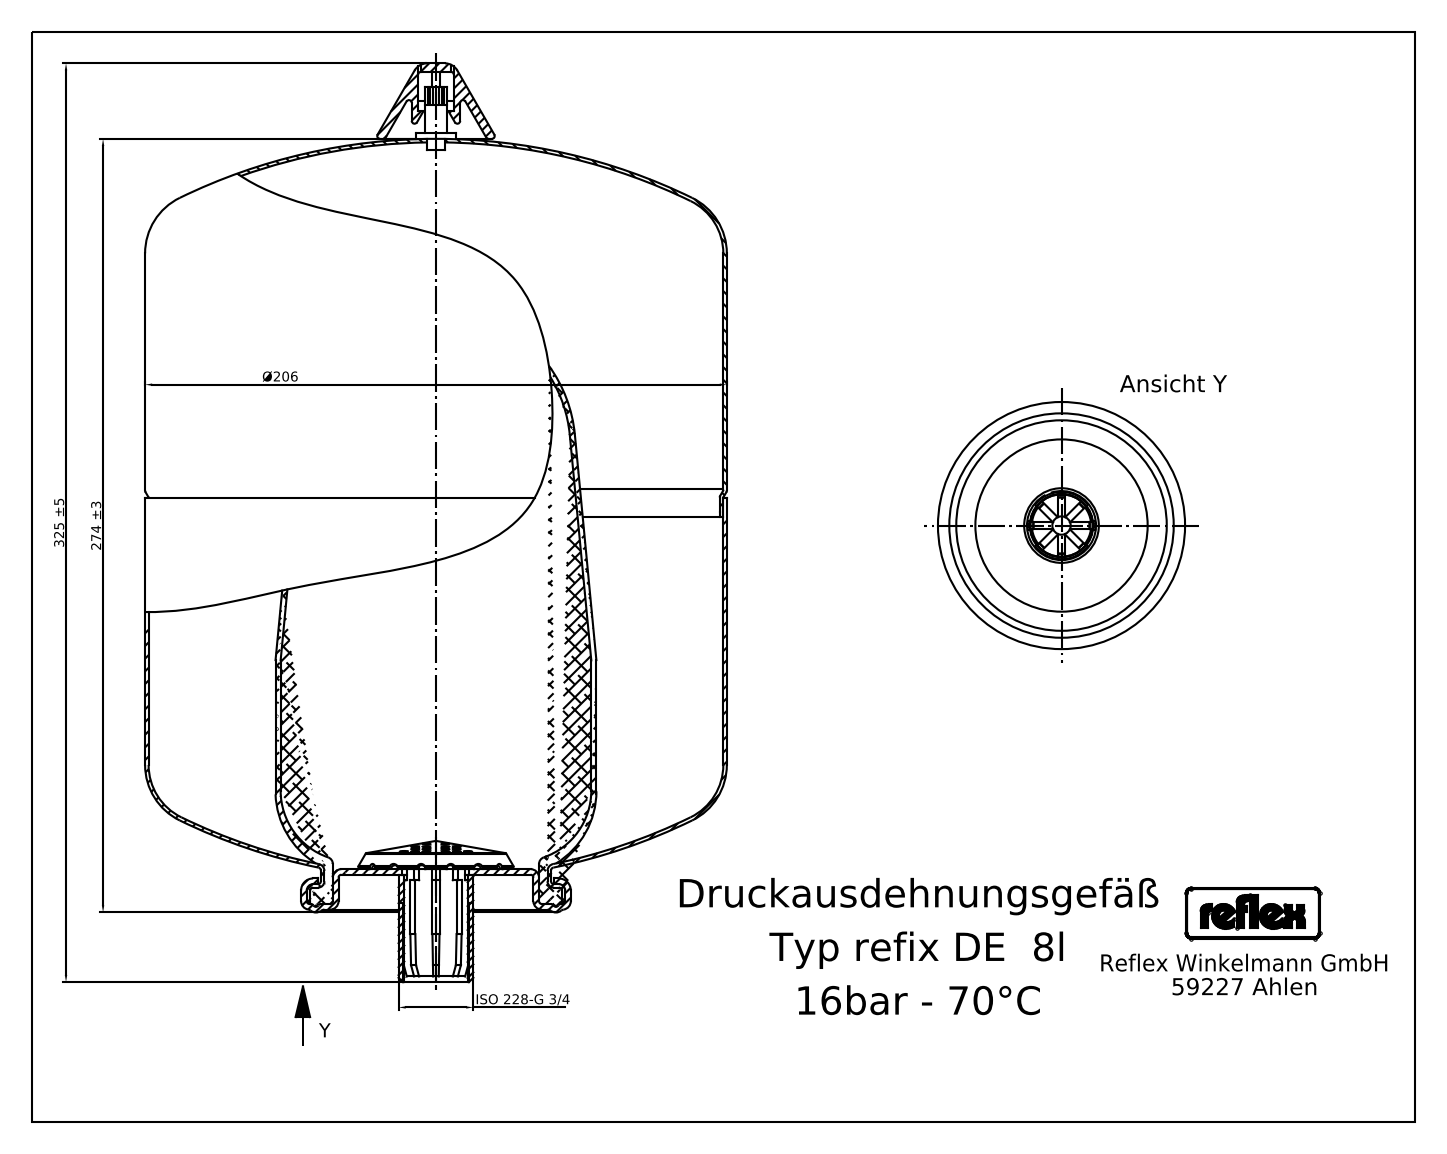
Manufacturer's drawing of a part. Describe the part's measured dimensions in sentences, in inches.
Its 3-D file was written by "Mechanical Desktop 2008 (CONFIG_CONTROL_DESIGN)". It is 13 solids with 151 faces: 71 planar, 46 cylindrical and 34 other. Overall it measures 12.677 by 8.123 by 8.11 inches. Its volume is 476.8 cubic inches and its surface area 570 square inches. Round holes: 1 of diameter 0.555, 1 of diameter 0.744. Round bosses or shafts: 1 of diameter 8.11, 1 of diameter 3.78, 1 of diameter 3.228, 1 of diameter 1.059, 1 of diameter 0.673, 1 of diameter 0.354, 1 of diameter 0.236. Partial cylindrical surfaces (rounded edges, fillets, slot ends): 4 of radius 0.044, 3 of radius 0.018, 2 of radius 0.03, 2 of radius 0.053, 2 of radius 0.073, 2 of radius 0.074, 2 of radius 0.1, 1 of radius 0.022. The main face-to-face distances are 7.047, 1.299, 8.346, 0.512, 1.811, 8.858, 5.295, 4.783, 3.484, 3.563.
